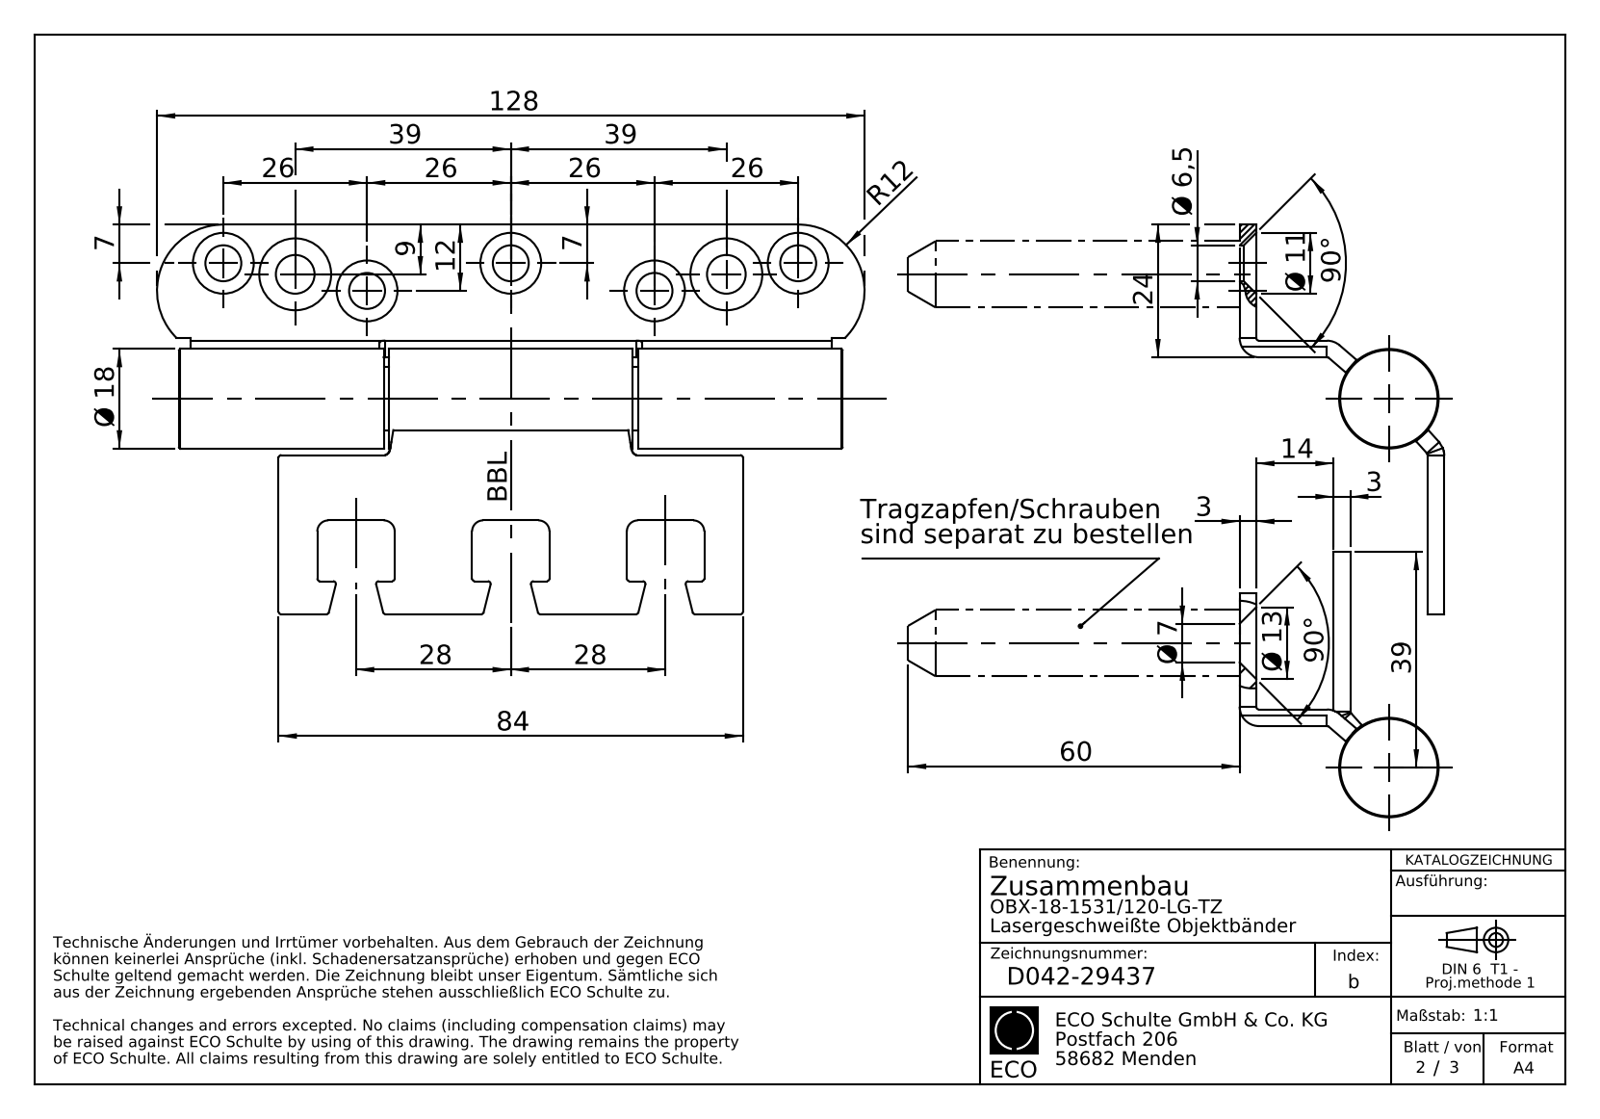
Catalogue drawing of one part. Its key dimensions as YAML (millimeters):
part_name: "D043-24250; D046-14312; D043-29438; DIN5401-III (+6 more)"
step_written_by: "SolidWorks 2020 (CONFIG_CONTROL_DESIGN)"
units: millimeters
bodies: {solids: 15, faces: 540, planar: 255, cylindrical: 158, other: 127}
overall_size: [128, 96, 48]
volume: 61549
surface_area: 36302
round_holes:
  - {diameter: 6.5, count: 5}
  - {diameter: 2, count: 2}
  - {diameter: 5, count: 2}
  - {diameter: 0.5, count: 1}
  - {diameter: 4.5, count: 1}
  - {diameter: 7.9, count: 1}
round_bosses_or_shafts:
  - {diameter: 12, count: 3}
  - {diameter: 6, count: 2}
  - {diameter: 18, count: 1}
  - {diameter: 11.8, count: 1}
  - {diameter: 11.5, count: 1}
  - {diameter: 7.7, count: 1}
  - {diameter: 4, count: 1}
  - {diameter: 1.65, count: 1}
partial_cylinders:
  - {radius: 0.5, count: 25}
  - {radius: 0.25, count: 6}
  - {radius: 2, count: 6}
  - {radius: 3.5, count: 3}
  - {radius: 0.68, count: 2}
  - {radius: 2.1, count: 2}
  - {radius: 3, count: 2}
  - {radius: 12, count: 2}
face_to_face_distances: [3, 17, 20, 14, 11.5, 82, 108.5, 25.5, 21, 24]
hole_center_spacings: [26.48, 52, 13.15, 13.34, 39.05, 65.07, 78.16, 91.02]
